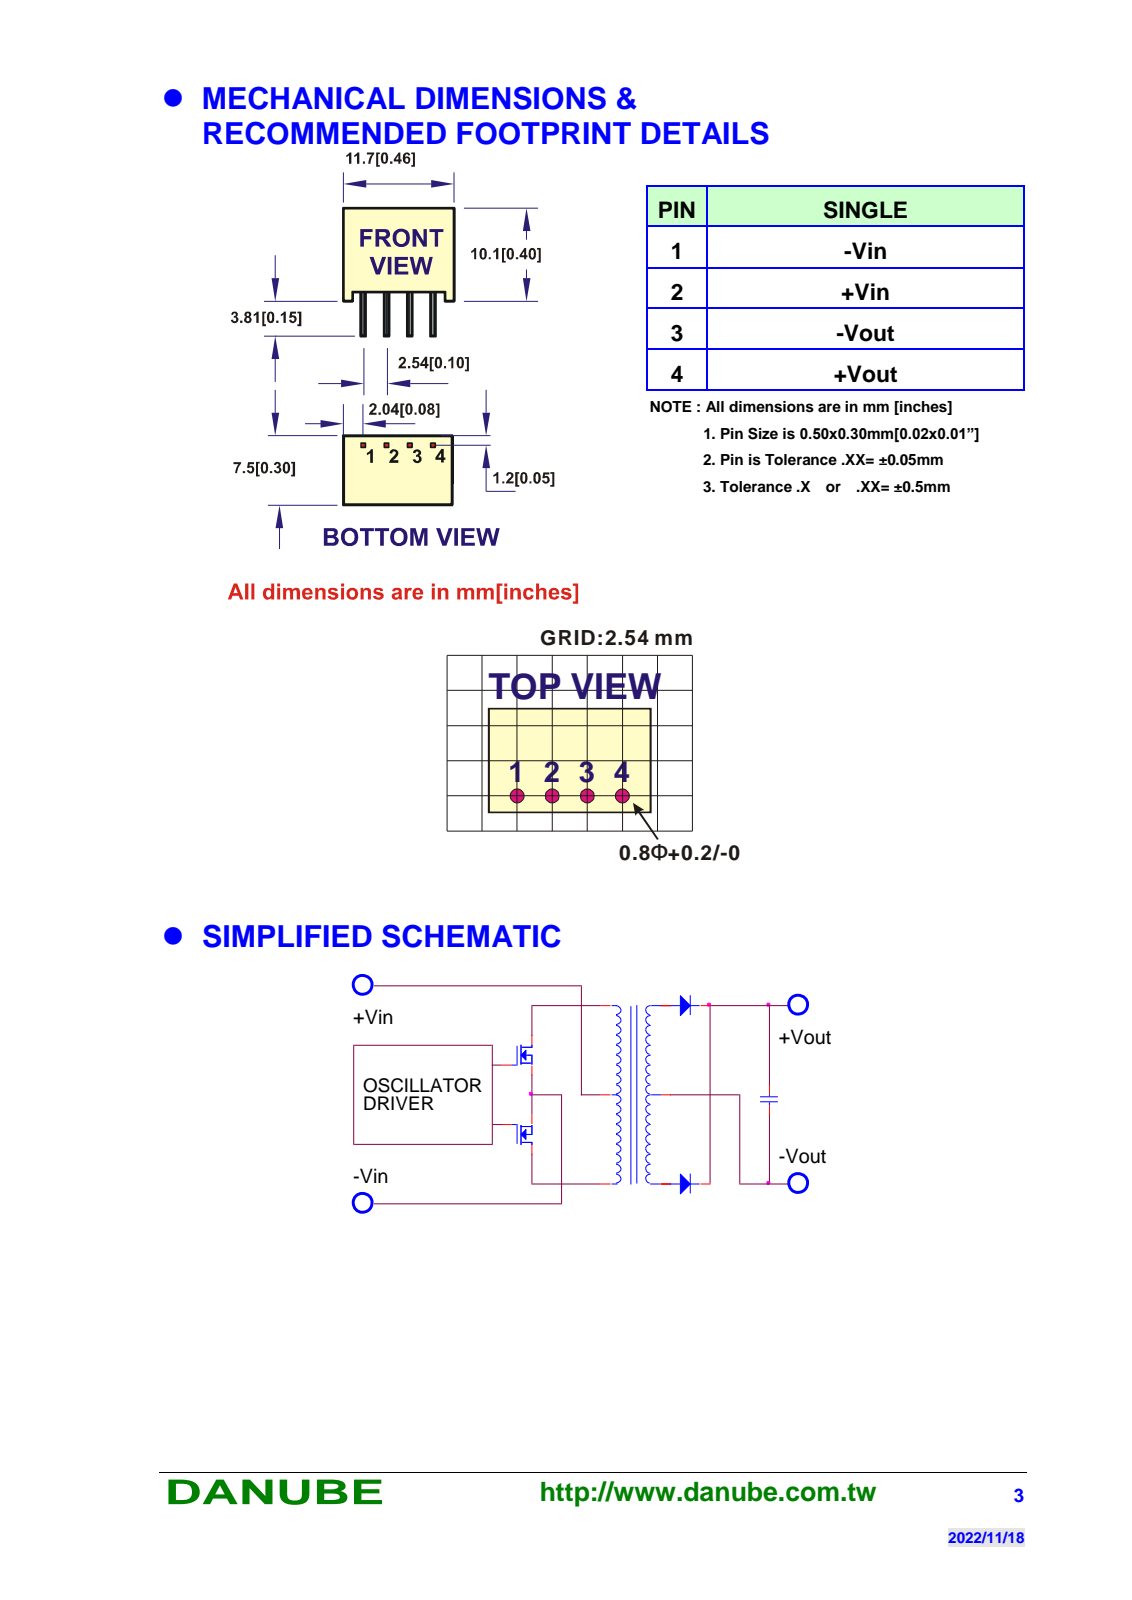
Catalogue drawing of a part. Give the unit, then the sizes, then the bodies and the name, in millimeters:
Units: millimetres
Overall size (bounding box): 13.91 × 11.7 × 7.5
Main face-to-face distances: 7.5, 9.6, 11.7, 0.5, 6.6, 0.9, 6.3, 1.2, 2.54, 10.1
Volume: 849 mm³ · Surface area: 589 mm²
Bodies: 5 solids, 40 faces (40 planar, 0 cylindrical, 0 other)
Part name (STEP PRODUCT): case; pin_1; pin_4; pin_2 (+1 more)
STEP written by: FreeCAD (AUTOMOTIVE_DESIGN)
